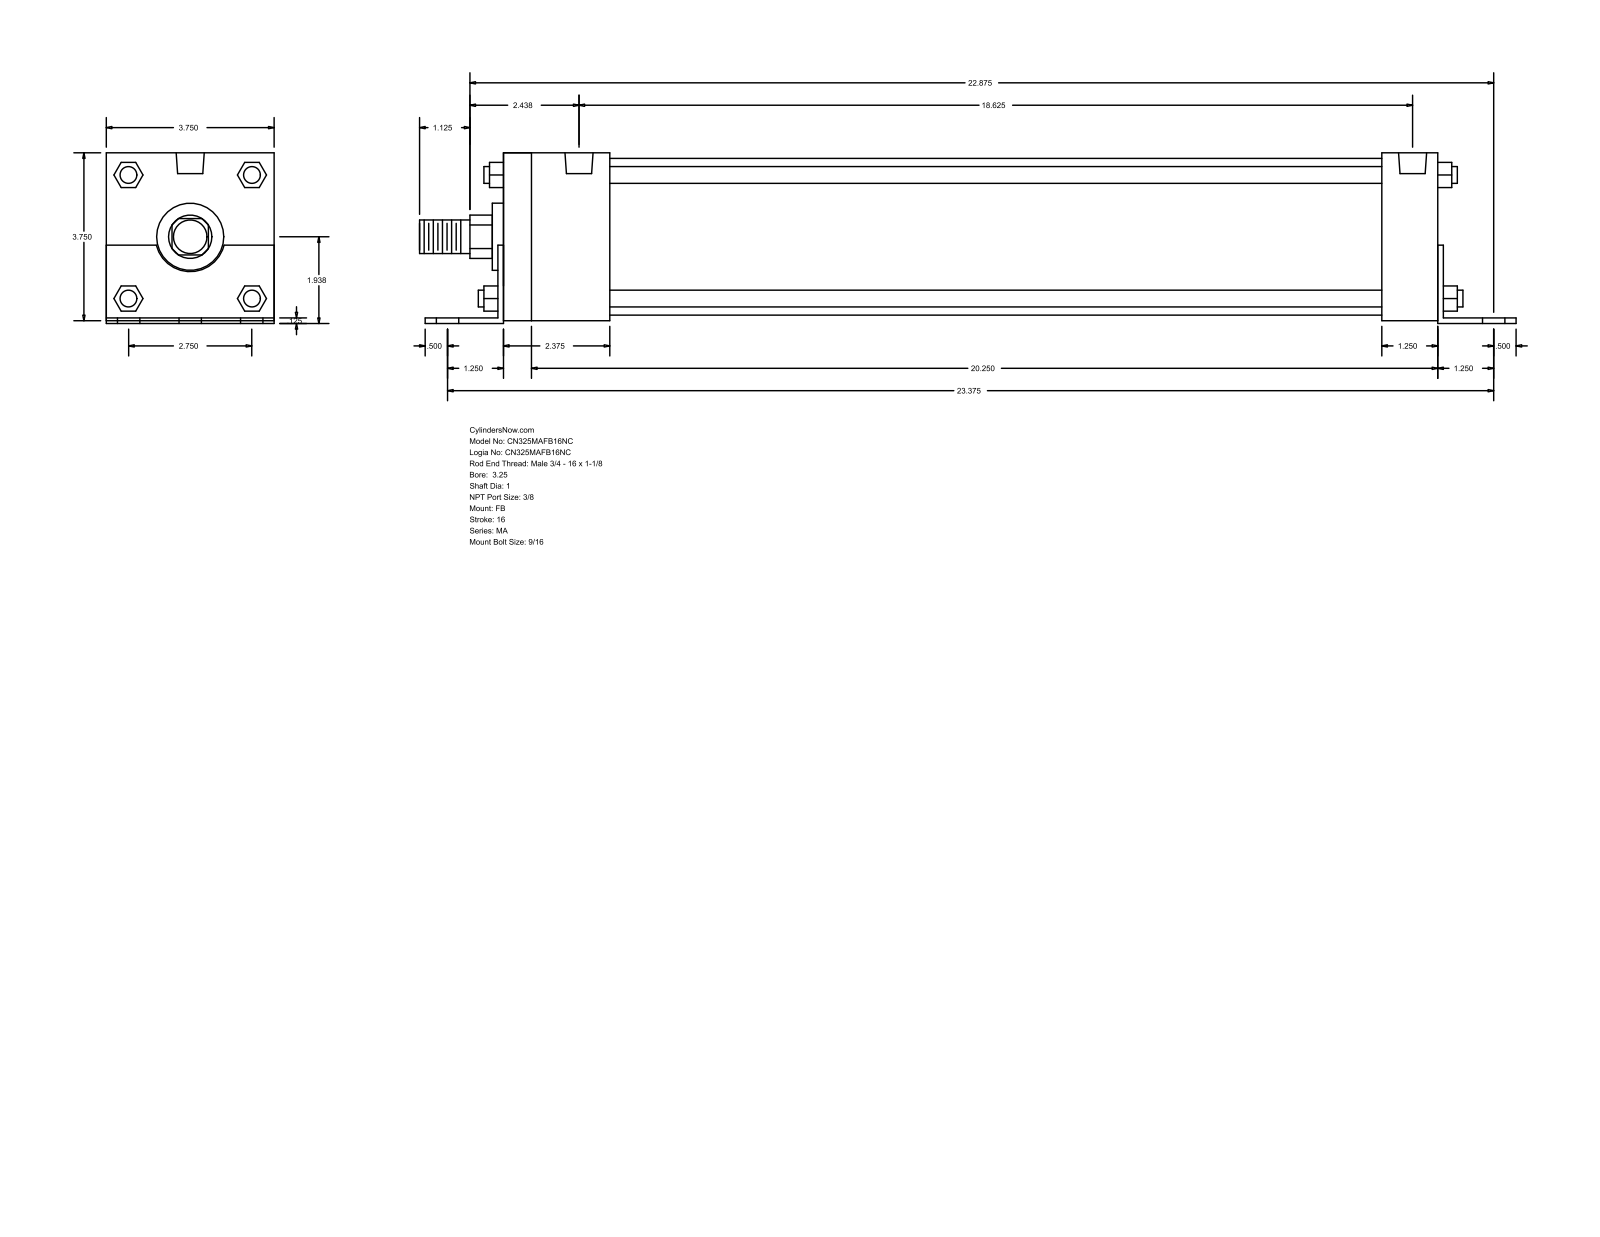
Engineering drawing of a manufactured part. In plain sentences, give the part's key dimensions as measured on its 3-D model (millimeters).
The part is named "MA_FB__0325_1". Its 3-D file was written by "GSSL Pune (CONFIG_CONTROL_DESIGN)". It is 0 solids with 140 faces: 105 planar, 35 cylindrical and 0 other. Overall it measures 622.3 by 96.84 by 95.25 millimeters. Round holes: 6 of diameter 14.29, 4 of diameter 11.11, 2 of diameter 15.93. Round bosses or shafts: 4 of diameter 9.53, 1 of diameter 88.9, 1 of diameter 38.1, 1 of diameter 25.4, 1 of diameter 19.05. Partial cylindrical surfaces (rounded edges, fillets, slot ends): 1 of radius 12.29, 1 of radius 19.81. The main face-to-face distances are 95.24, 3.17, 1.59, 96.83, 1.58, 93.66, 3.18, 530.22, 536.57, 533.4. The hole center spacings are 34.92, 594.75, 593.72, 4.76, 57.78, 61.64, 69.84, 82.38.
